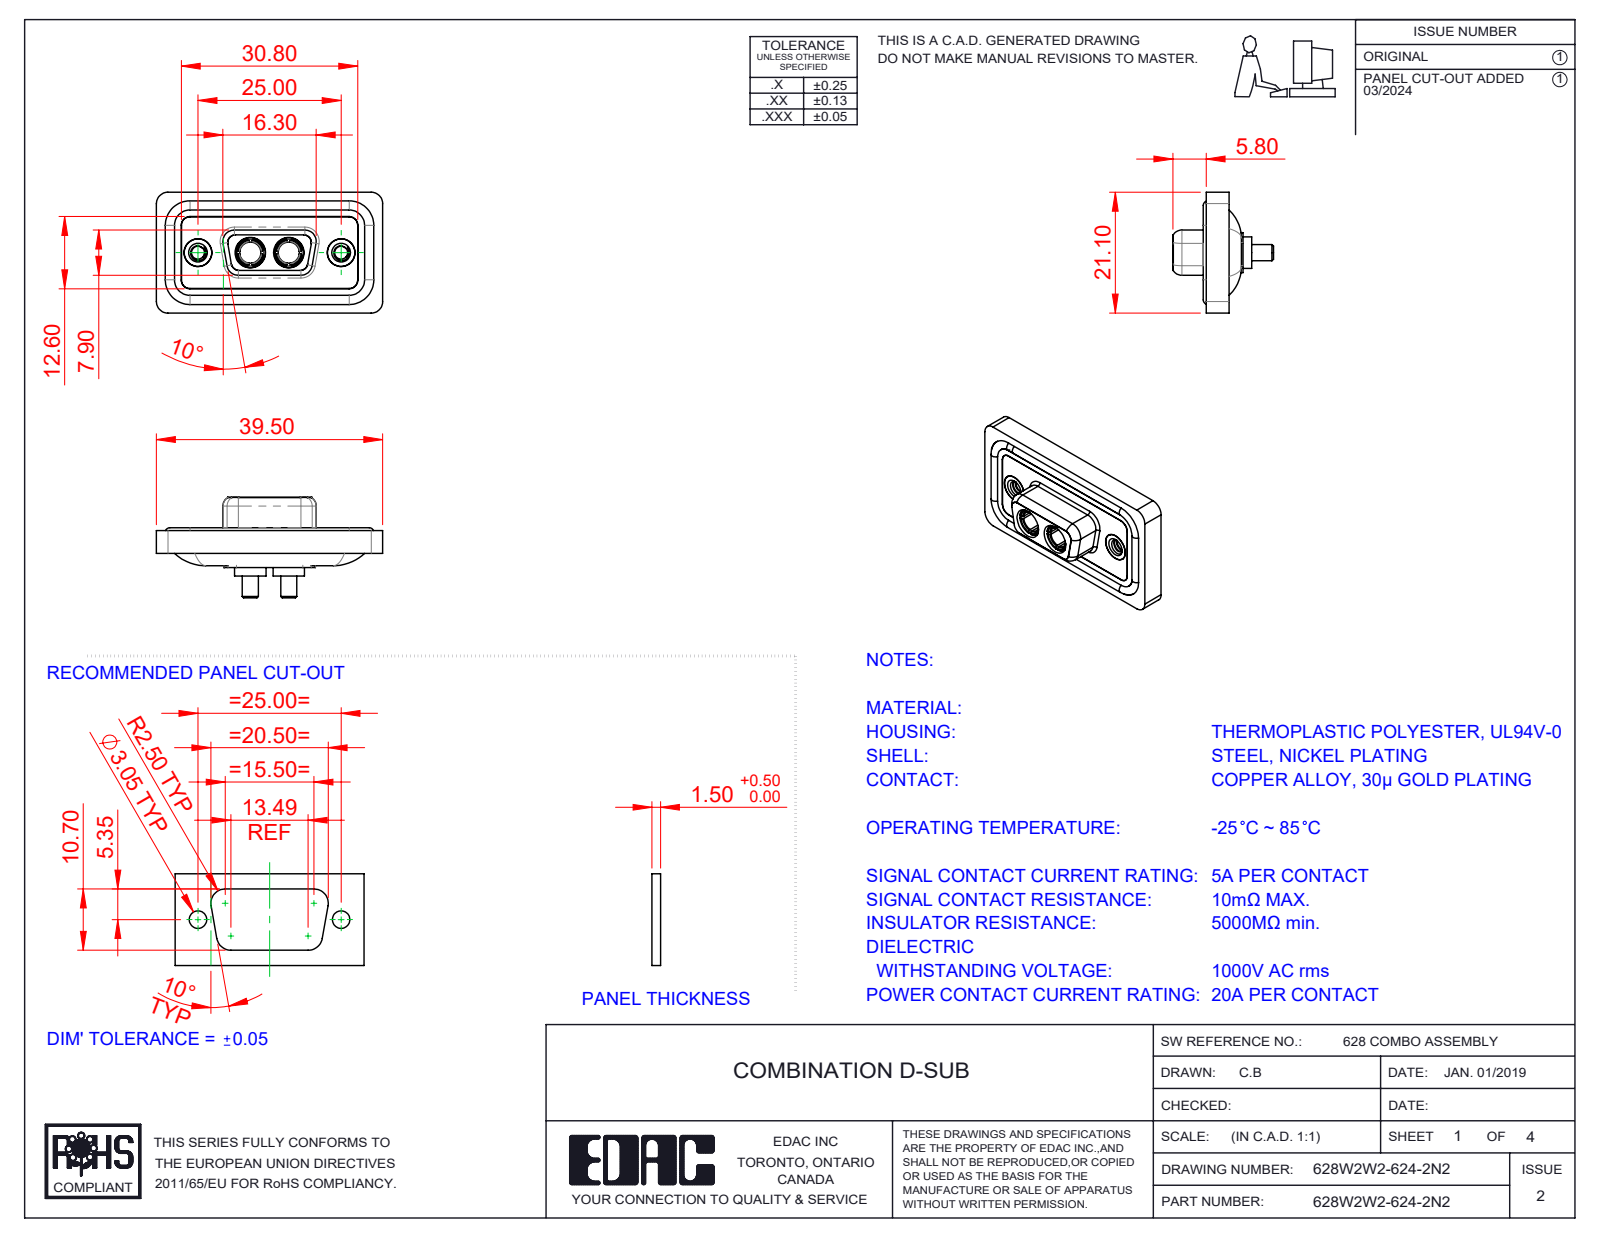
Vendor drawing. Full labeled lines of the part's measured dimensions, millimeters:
Part name (STEP PRODUCT): 628Combo Shell Rear_09 Contacts; 628Combo Threaded Rivet_2; 628W2W2-624-2N2; 628Combo Waterproof Housing_09 Contacts (+3 more)
STEP written by: SolidWorks 2023 (CONFIG_CONTROL_DESIGN)
Units: millimetres
Bodies: 11 solids, 534 faces (163 planar, 234 cylindrical, 137 other)
Overall size (bounding box): 39.5 × 21.1 × 17.55
Volume: 4 713 mm³ · Surface area: 7 636 mm²
Round holes (diameter × count): ⌀4.85 ×4, ⌀2.26 ×2, ⌀3.7 ×2, ⌀4 ×2, ⌀4.05 ×2, ⌀5 ×2, ⌀5.3 ×2
Round bosses / shafts (diameter × count): ⌀1.6 ×4, ⌀5.5 ×2, ⌀5.2 ×2, ⌀4.96 ×2, ⌀4.95 ×2, ⌀4.8 ×2, ⌀4.75 ×2, ⌀3.75 ×2
Partial cylindrical surfaces — rounded edges, fillets, slot ends (radius × count): R1.5 ×22, R2 ×18, R1.35 ×8, R1.6 ×8, R0.25 ×4, R0.5 ×4, R0.6 ×4, R0.65 ×4
Main face-to-face distances: 0.4, 1.8, 1.1, 2.9, 0.5, 1.6, 5.65, 7.45, 1.5, 5.35
Hole centre spacings: 9.14, 15.86, 6.72, 25
